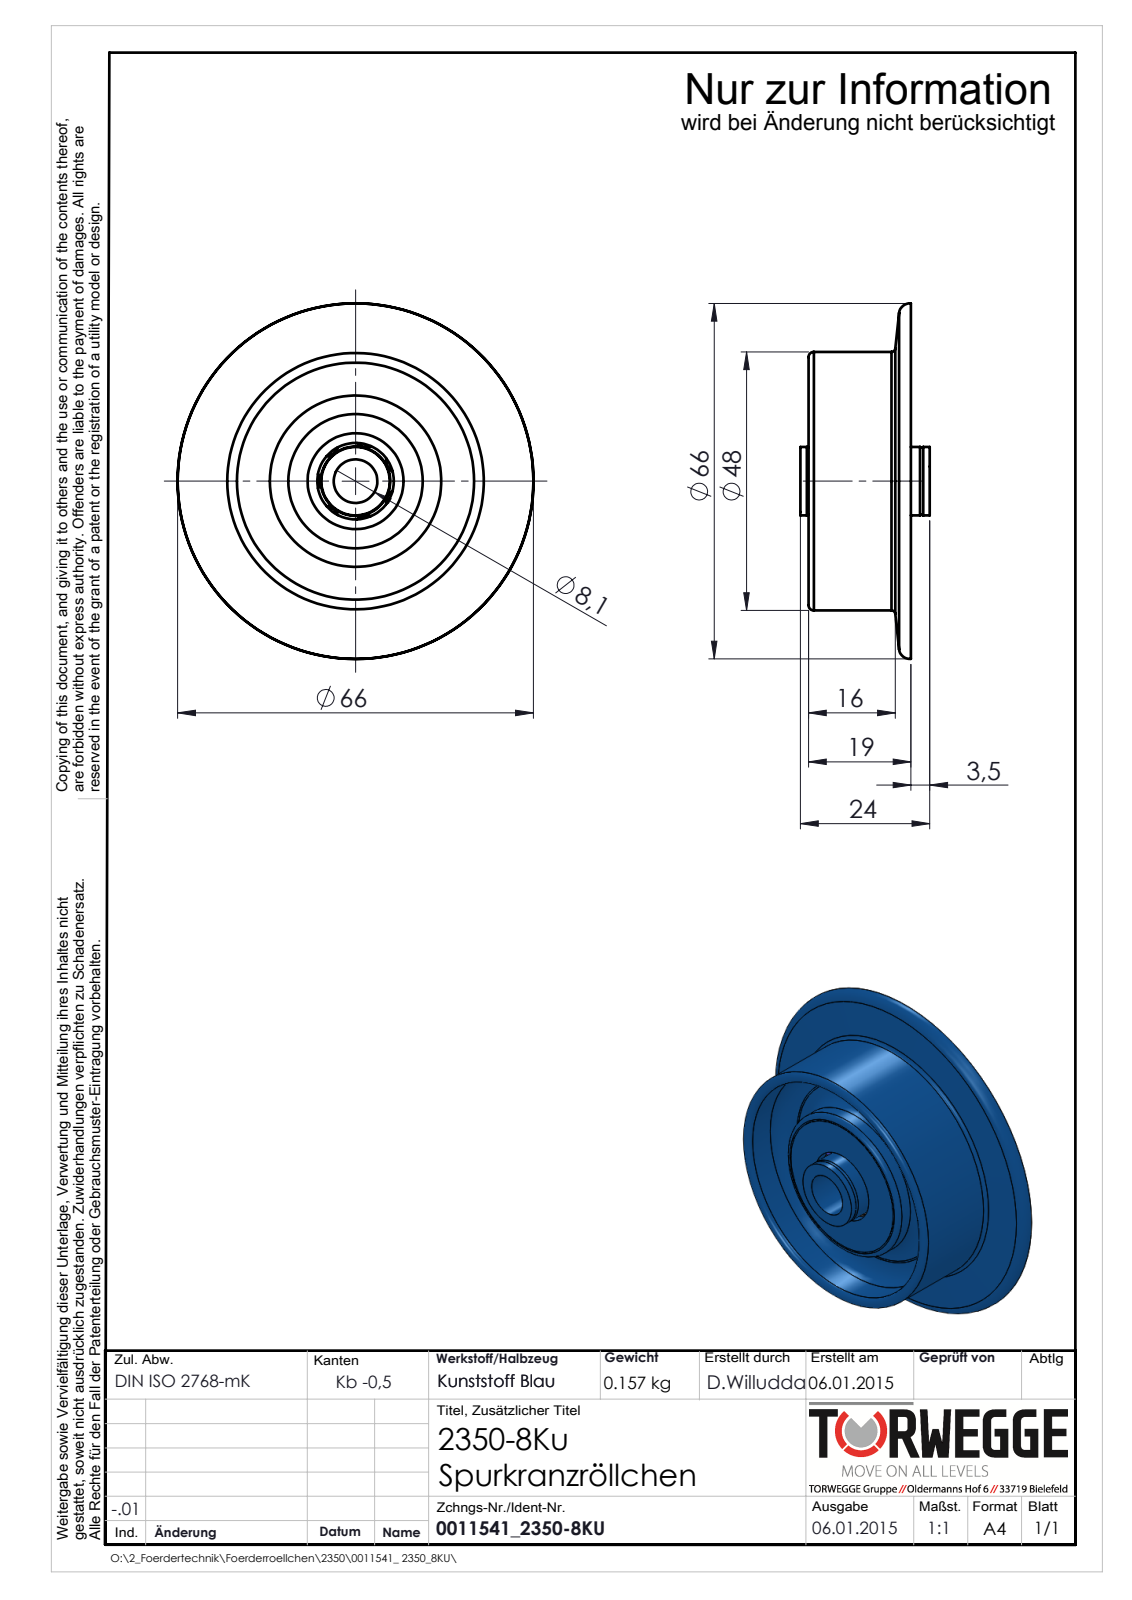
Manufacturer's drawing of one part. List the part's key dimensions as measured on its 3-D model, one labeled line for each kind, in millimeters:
Part name (STEP PRODUCT): 0011541_2350-8KU
STEP written by: SolidWorks 2014 (AUTOMOTIVE_DESIGN)
Units: millimetres
Bodies: 0 solids, 102 faces (12 planar, 34 cylindrical, 56 other)
Overall size (bounding box): 66.02 × 66.02 × 24
Round holes (diameter × count): ⌀8.1 ×1, ⌀14 ×1, ⌀14.2 ×1, ⌀15.85 ×1, ⌀26.8 ×1, ⌀44 ×1
Round bosses / shafts (diameter × count): ⌀48 ×1, ⌀29.36 ×1, ⌀12.7 ×1
Main face-to-face distances: 3.9, 20.1, 16.2, 24, 10.6, 6.7, 9.5, 13.4, 8.4, 16.3
